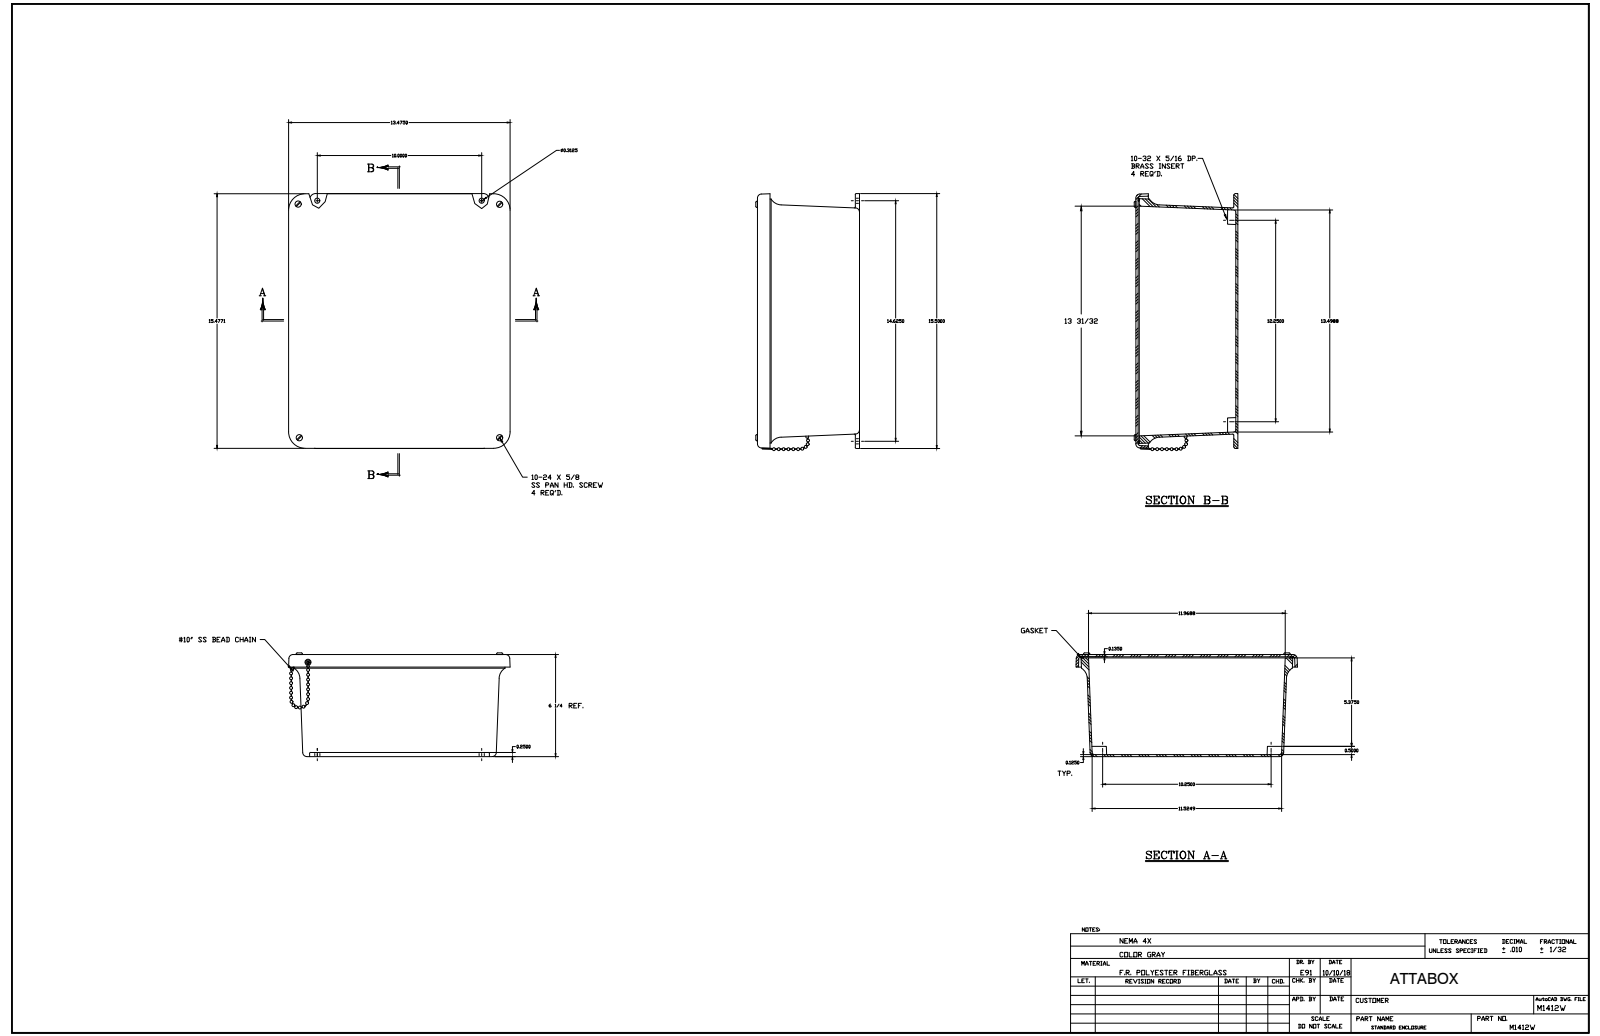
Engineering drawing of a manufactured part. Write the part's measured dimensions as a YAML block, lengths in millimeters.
part_name: "M1412W"
step_written_by: "SolidWorks 2018 (AUTOMOTIVE_DESIGN)"
units: millimeters
bodies: {solids: 45, faces: 898, planar: 191, cylindrical: 295, other: 412}
overall_size: [407.5, 347.8, 160.8]
volume: 1840000
surface_area: 988400
round_holes:
  - {diameter: 3.9, count: 8}
  - {diameter: 3.6, count: 6}
  - {diameter: 3.7, count: 4}
  - {diameter: 4, count: 4}
  - {diameter: 5.5, count: 4}
  - {diameter: 4.7, count: 2}
  - {diameter: 3.2, count: 1}
round_bosses_or_shafts:
  - {diameter: 6.9, count: 8}
  - {diameter: 4.8, count: 4}
  - {diameter: 4, count: 4}
  - {diameter: 9.5, count: 2}
  - {diameter: 6.4, count: 2}
  - {diameter: 3.2, count: 2}
  - {diameter: 7.2, count: 1}
partial_cylinders:
  - {radius: 0.8, count: 20}
  - {radius: 3.2, count: 12}
  - {radius: 6.4, count: 12}
  - {radius: 5.1, count: 8}
  - {radius: 9.5, count: 4}
  - {radius: 19.1, count: 4}
  - {radius: 0.3, count: 2}
  - {radius: 1.6, count: 2}
face_to_face_distances: [3.2, 3.4, 154, 157.5, 150.9, 154.3, 3.2, 8.4, 1.6, 152.4]
hole_center_spacings: [34.8, 286, 336.7, 440.4, 82.6, 165.1, 260.4, 309.5]
